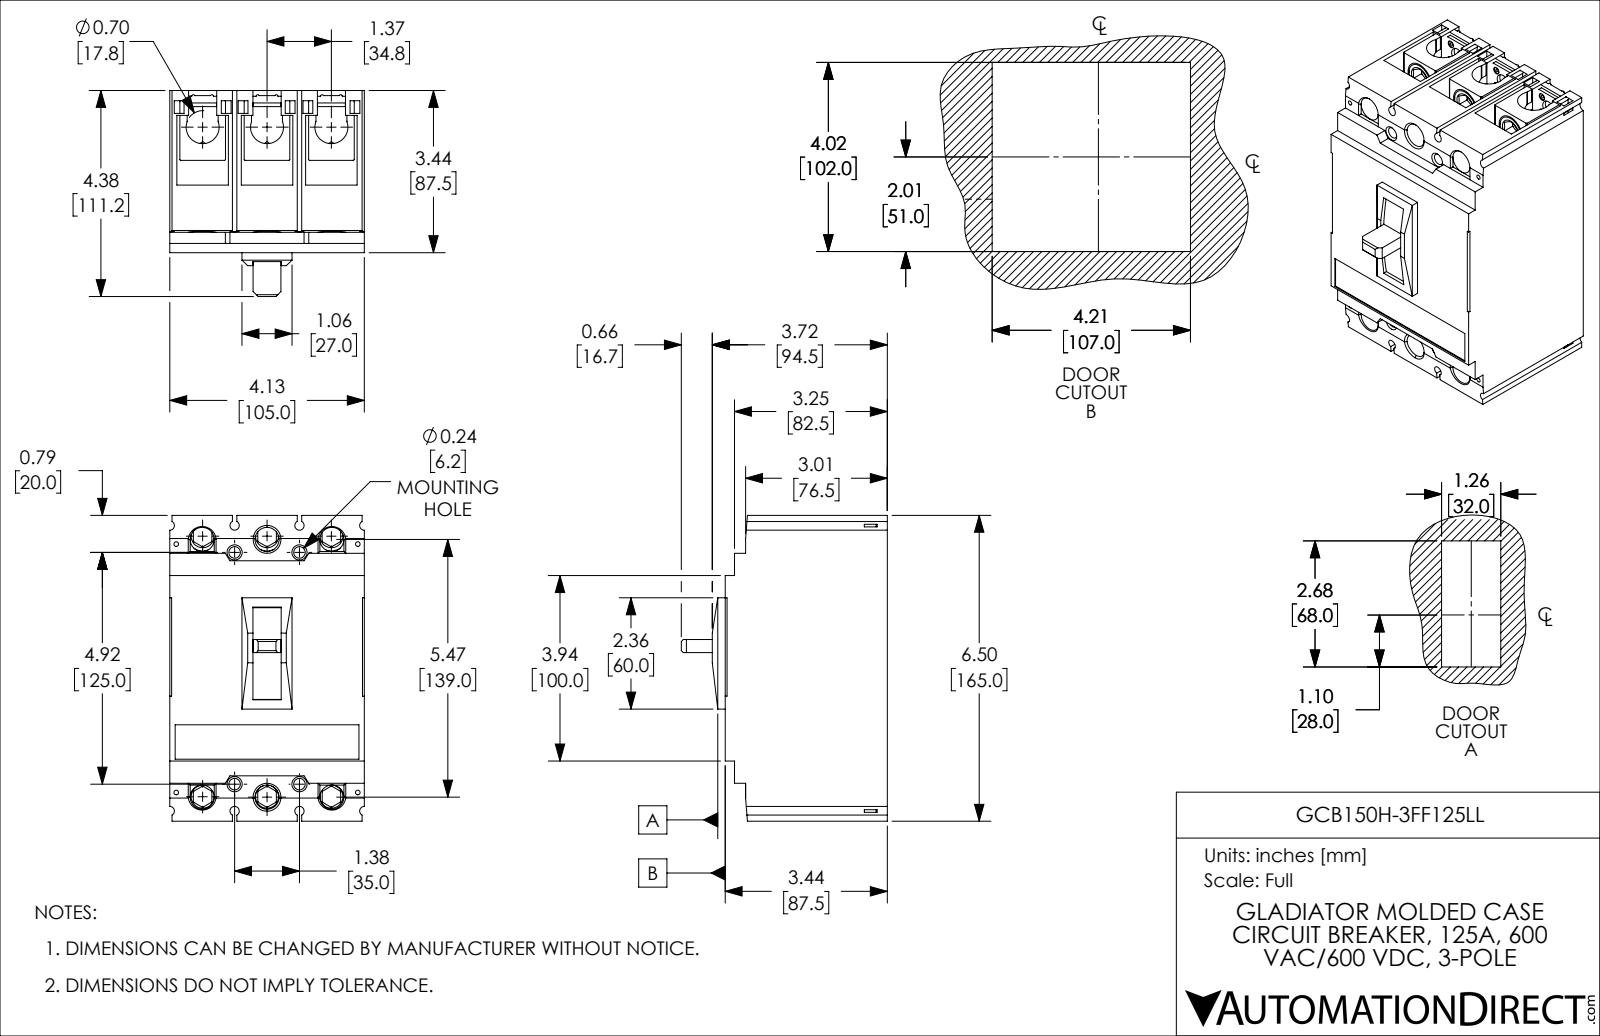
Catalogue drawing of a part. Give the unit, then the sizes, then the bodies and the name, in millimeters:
Units: millimetres
Overall size (bounding box): 165 × 111.2 × 105
Round holes (diameter × count): ⌀1.7 ×24, ⌀4 ×24, ⌀2.5 ×10, ⌀9 ×6, ⌀13 ×6, ⌀17.5 ×6, ⌀5 ×4, ⌀6.2 ×4
Round bosses / shafts (diameter × count): ⌀18 ×6
Partial cylindrical surfaces — rounded edges, fillets, slot ends (radius × count): R1 ×36, R0.2 ×24, R0.4 ×6, R0.5 ×6, R0.8 ×6, R2.5 ×4, R8.9 ×3, R143.2 ×1
Main face-to-face distances: 34.7, 105, 1.6, 26.2, 21.5, 22, 87.5, 143, 69.5, 6.7
Hole centre spacings: 35, 7.2, 34.7, 14.5, 18.8, 19.1, 133.1, 147.5
Volume: 1 312 000 mm³ · Surface area: 160 100 mm²
Bodies: 19 solids, 1004 faces (544 planar, 381 cylindrical, 79 other)
Part name (STEP PRODUCT): GCB150H-3FF125LL
STEP written by: SolidWorks 2021 (CONFIG_CONTROL_DESIGN)
